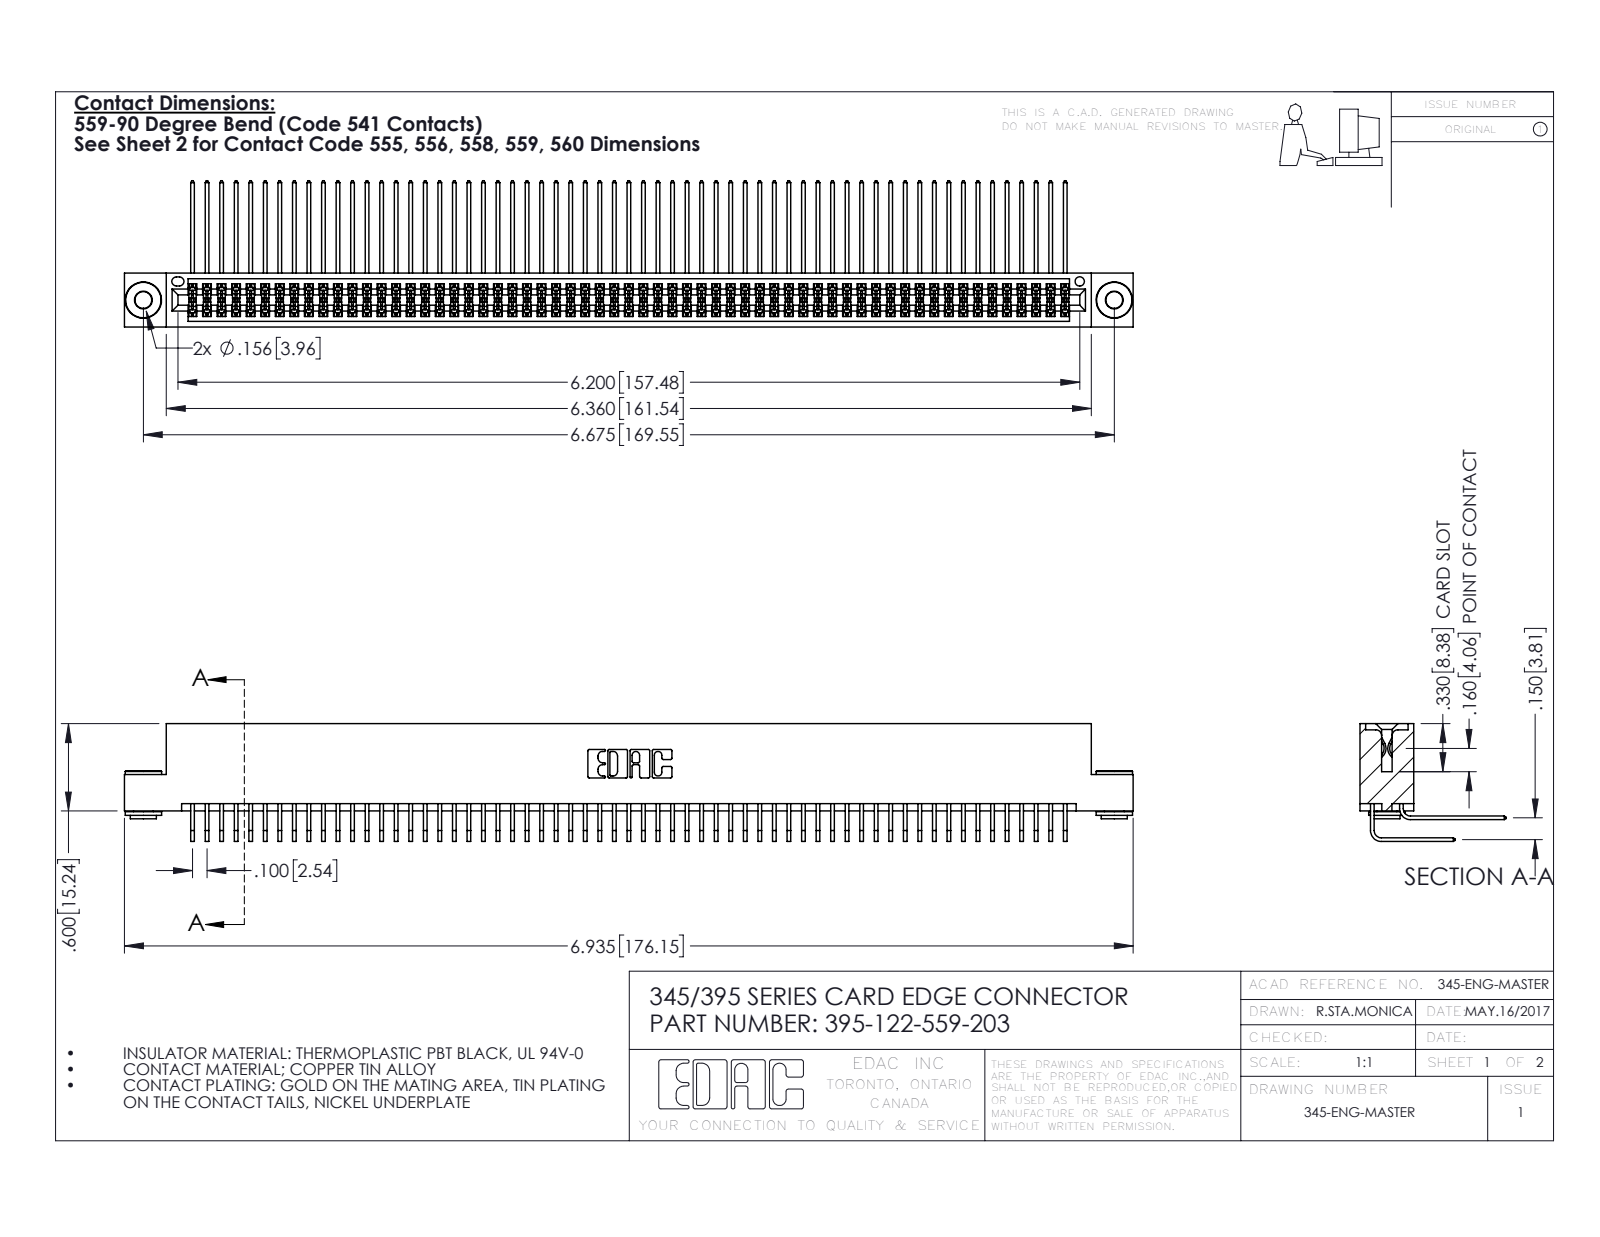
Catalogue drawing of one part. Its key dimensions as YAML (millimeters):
part_name: "345 Part_Flush Mounting Lugs - 0.156 Dia-TH; 345-292-001_558 559 Tail - 1; 345-250-002_345-250-002-102; 345-292-001_559 Tail - 2 (+1 more)"
step_written_by: "SolidWorks 2016 (CONFIG_CONTROL_DESIGN)"
units: millimeters
bodies: {solids: 125, faces: 6508, planar: 4360, cylindrical: 2140, other: 8}
overall_size: [176.1, 25.5, 20.5]
volume: 18010
surface_area: 30500
round_holes:
  - {diameter: 2.9, count: 2}
  - {diameter: 4, count: 2}
  - {diameter: 1.6, count: 1}
round_bosses_or_shafts:
  - {diameter: 6.4, count: 2}
  - {diameter: 4.6, count: 2}
  - {diameter: 3.5, count: 2}
partial_cylinders:
  - {radius: 0.2, count: 183}
  - {radius: 0.3, count: 22}
  - {radius: 0.2, count: 6}
  - {radius: 0.8, count: 6}
  - {radius: 0.7, count: 3}
  - {radius: 0.4, count: 2}
  - {radius: 0.5, count: 2}
  - {radius: 0.6, count: 2}
face_to_face_distances: [1.8, 7.6, 5.1, 9.4, 0.6, 2.5, 6.9, 5.7, 4.4, 3.8]
hole_center_spacings: [6.9, 163.6, 169.5]
